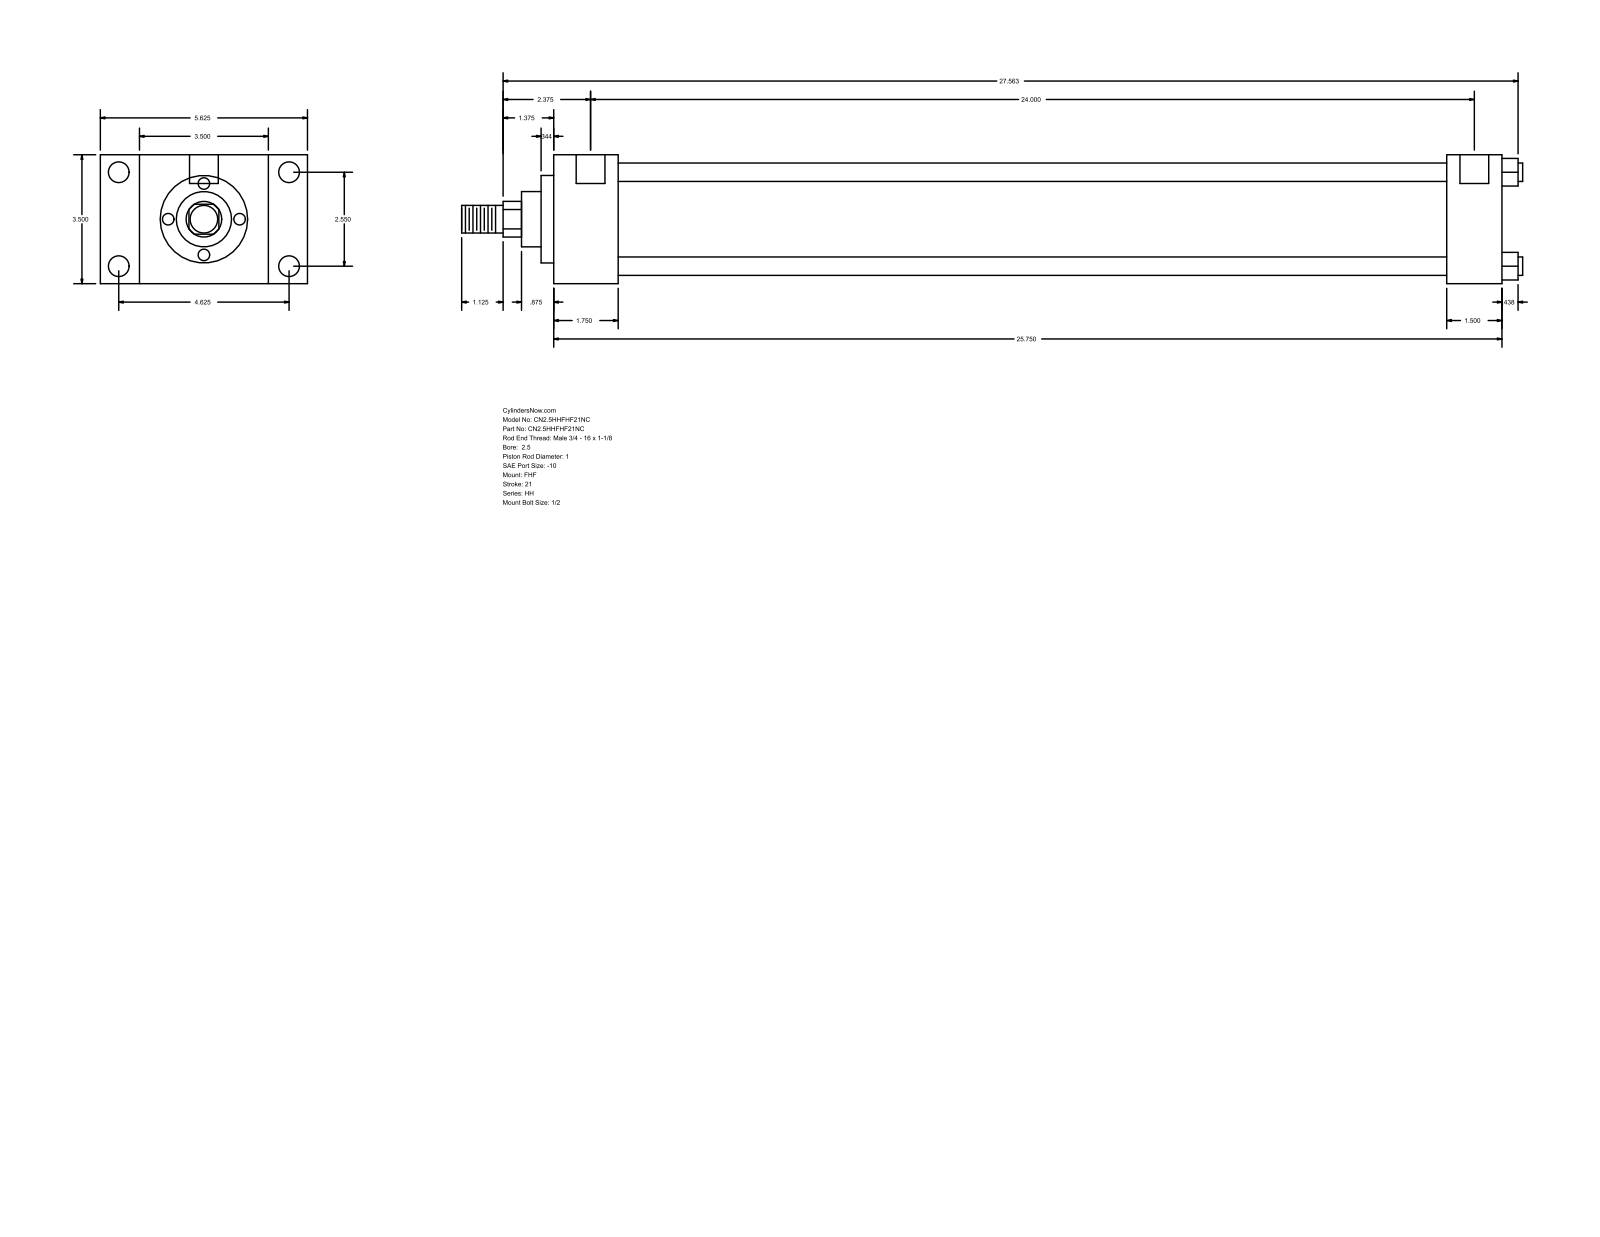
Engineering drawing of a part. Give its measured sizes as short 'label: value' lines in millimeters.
name: HH_FHF__0250_1
written by: GSSL Pune (CONFIG_CONTROL_DESIGN)
unit: mm
bodies: 0 solids, 90 faces (61 planar, 29 cylindrical, 0 other)
size: 731.84 × 142.88 × 88.9
holes: 4× ⌀5.56, 4× ⌀14.3, 2× ⌀19.84
bosses: 4× ⌀12.7, 1× ⌀73.03, 1× ⌀60.33, 1× ⌀38.1, 1× ⌀25.4, 1× ⌀19.05
rounds: 1× R12.29
face distances: 88.9, 44.46, 26.99, 115.89, 654.06, 609.6, 142.88, 38.1, 615.96, 571.5
hole spacings: 1.59, 64.76, 117.48, 134.15, 611.18, 612.77, 609.59
